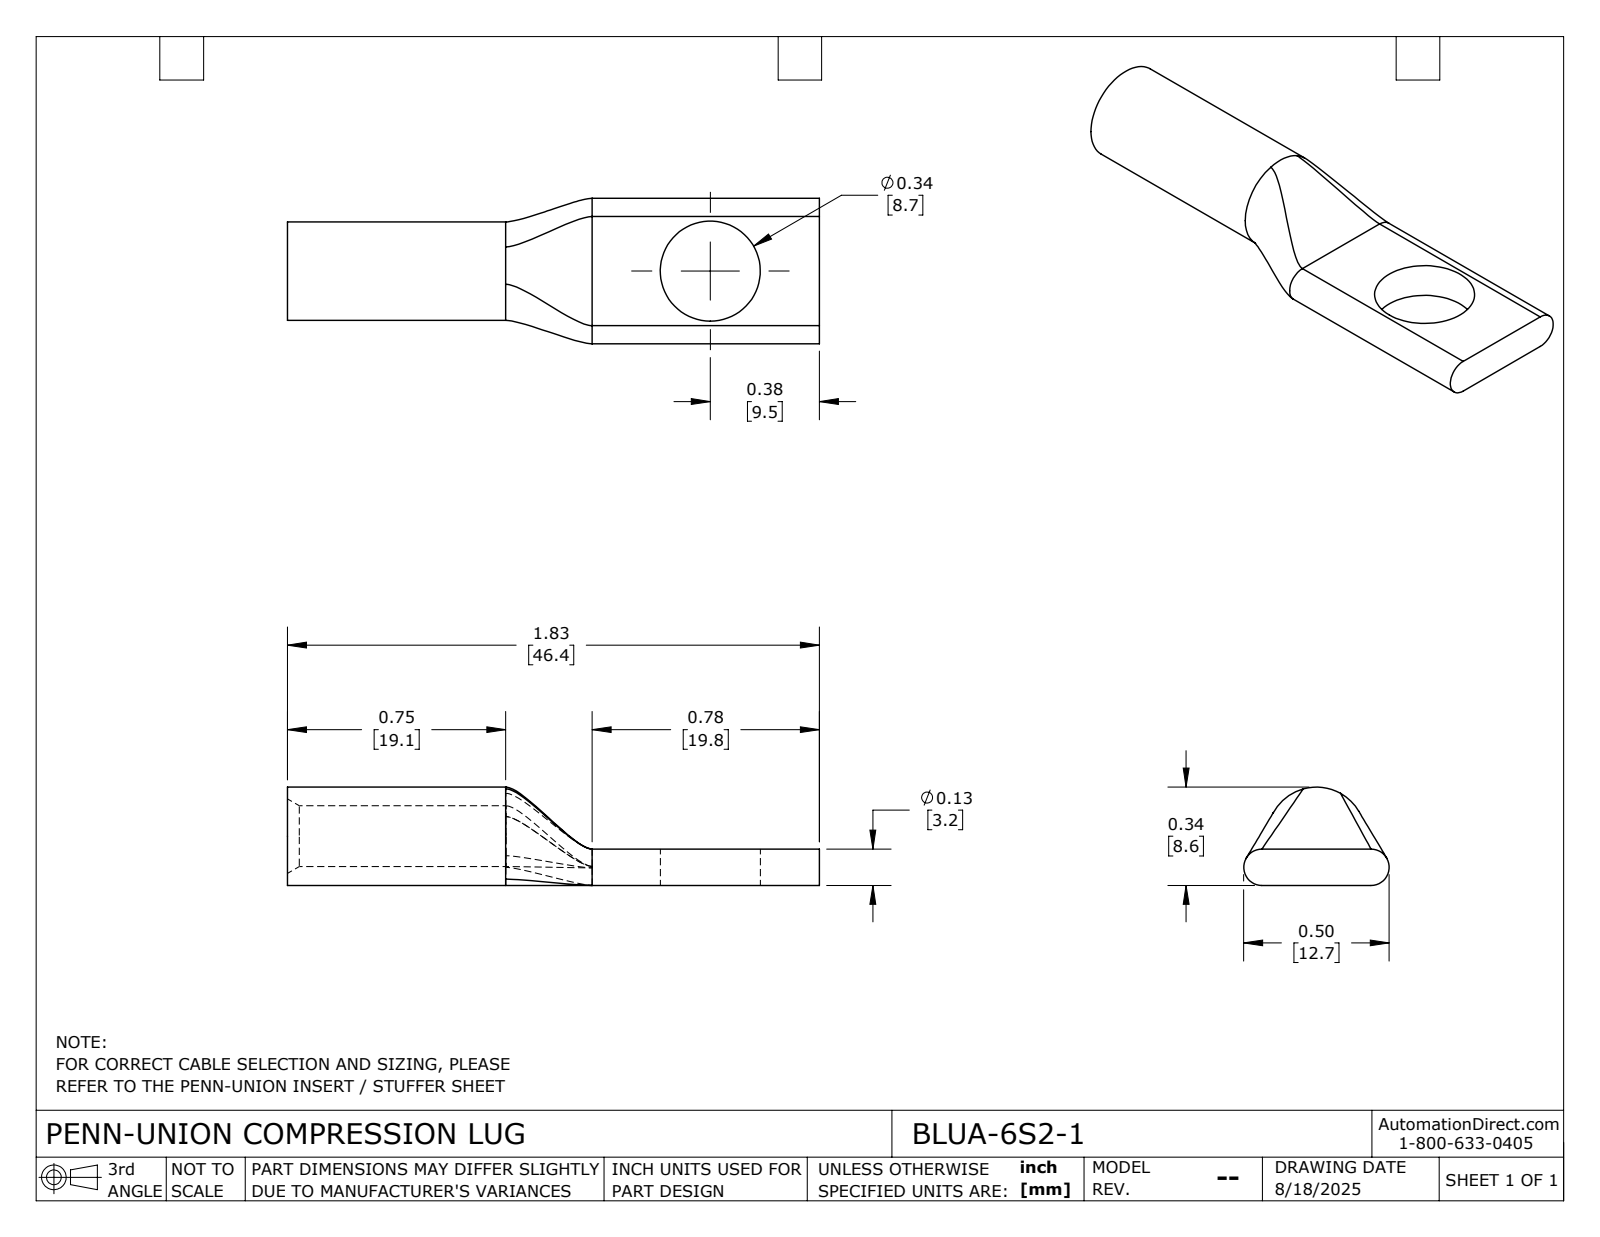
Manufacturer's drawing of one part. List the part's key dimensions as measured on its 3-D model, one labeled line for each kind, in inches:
Part name (STEP PRODUCT): BLUA-6S2-1
STEP written by: SolidWorks 2024 (CONFIG_CONTROL_DESIGN)
Units: inches
Bodies: 1 solid, 24 faces (5 planar, 9 cylindrical, 10 other)
Overall size (bounding box): 1.828 × 0.5 × 0.338
Volume: 0.093 in³ · Surface area: 2.813 in²
Round holes (diameter × count): ⌀0.209 ×1, ⌀0.344 ×1
Round bosses / shafts (diameter × count): ⌀0.338 ×1
Partial cylindrical surfaces — rounded edges, fillets, slot ends (radius × count): R0.062 ×2
Main face-to-face distances: 0.125, 1.828, 1.047, 0.781
